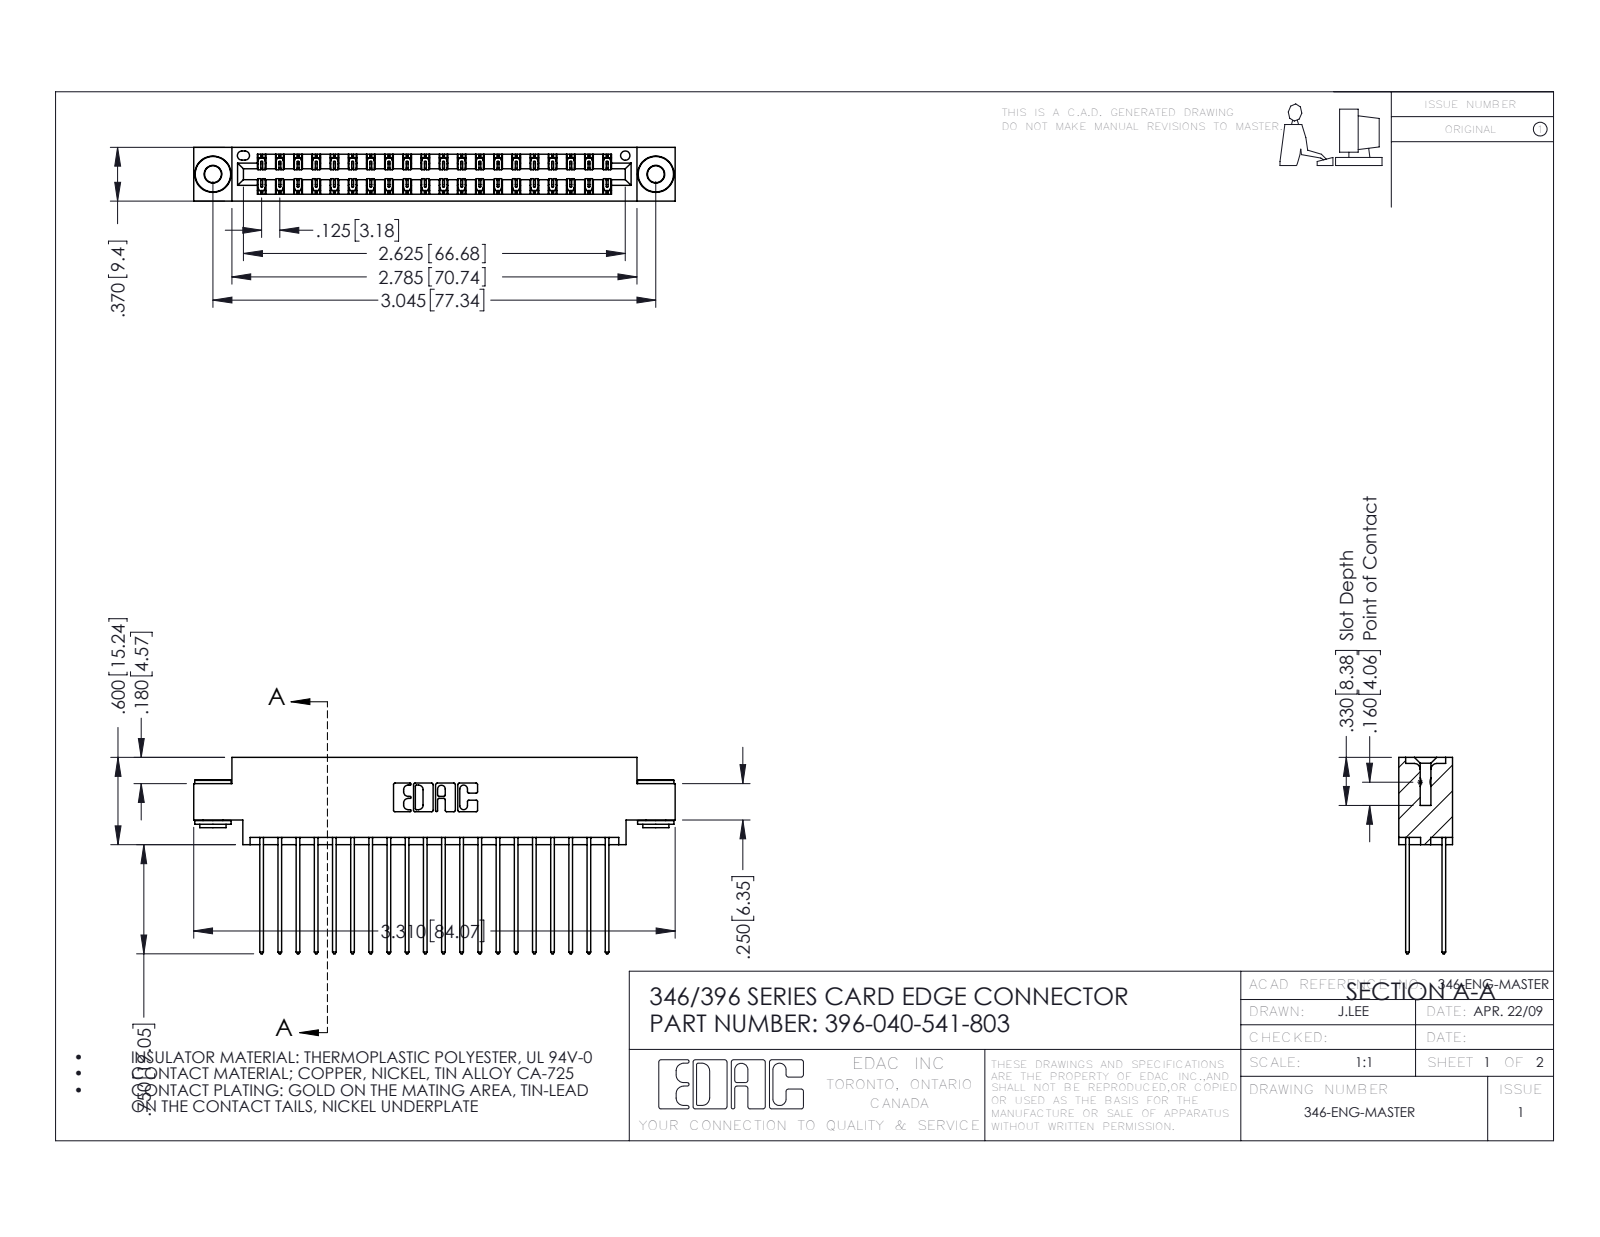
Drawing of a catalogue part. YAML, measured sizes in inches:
part_name: "345-292-001_345-293-141; 345-250-002_345-250-002-102; 346 Part_0.170 Offset - 0.156 Dia-TH; 396-040-541-803"
step_written_by: "SolidWorks 2016 (CONFIG_CONTROL_DESIGN)"
units: inches
bodies: {solids: 43, faces: 2244, planar: 1490, cylindrical: 746, other: 8}
overall_size: [3.31, 1.35, 0.37]
volume: 0.496
surface_area: 19.08
round_holes:
  - {diameter: 0.116, count: 2}
  - {diameter: 0.156, count: 2}
  - {diameter: 0.064, count: 1}
round_bosses_or_shafts:
  - {diameter: 0.25, count: 2}
  - {diameter: 0.18, count: 2}
  - {diameter: 0.136, count: 2}
partial_cylinders:
  - {radius: 0.006, count: 60}
  - {radius: 0.01, count: 40}
  - {radius: 0.01, count: 22}
  - {radius: 0.007, count: 6}
  - {radius: 0.031, count: 6}
  - {radius: 0.026, count: 3}
  - {radius: 0.014, count: 2}
  - {radius: 0.022, count: 2}
face_to_face_distances: [0.048, 0.322, 0.25, 0.025, 0.37, 0.072, 0.298, 0.275, 0.225, 0.148]
hole_center_spacings: [0.246, 2.837, 3.045]
